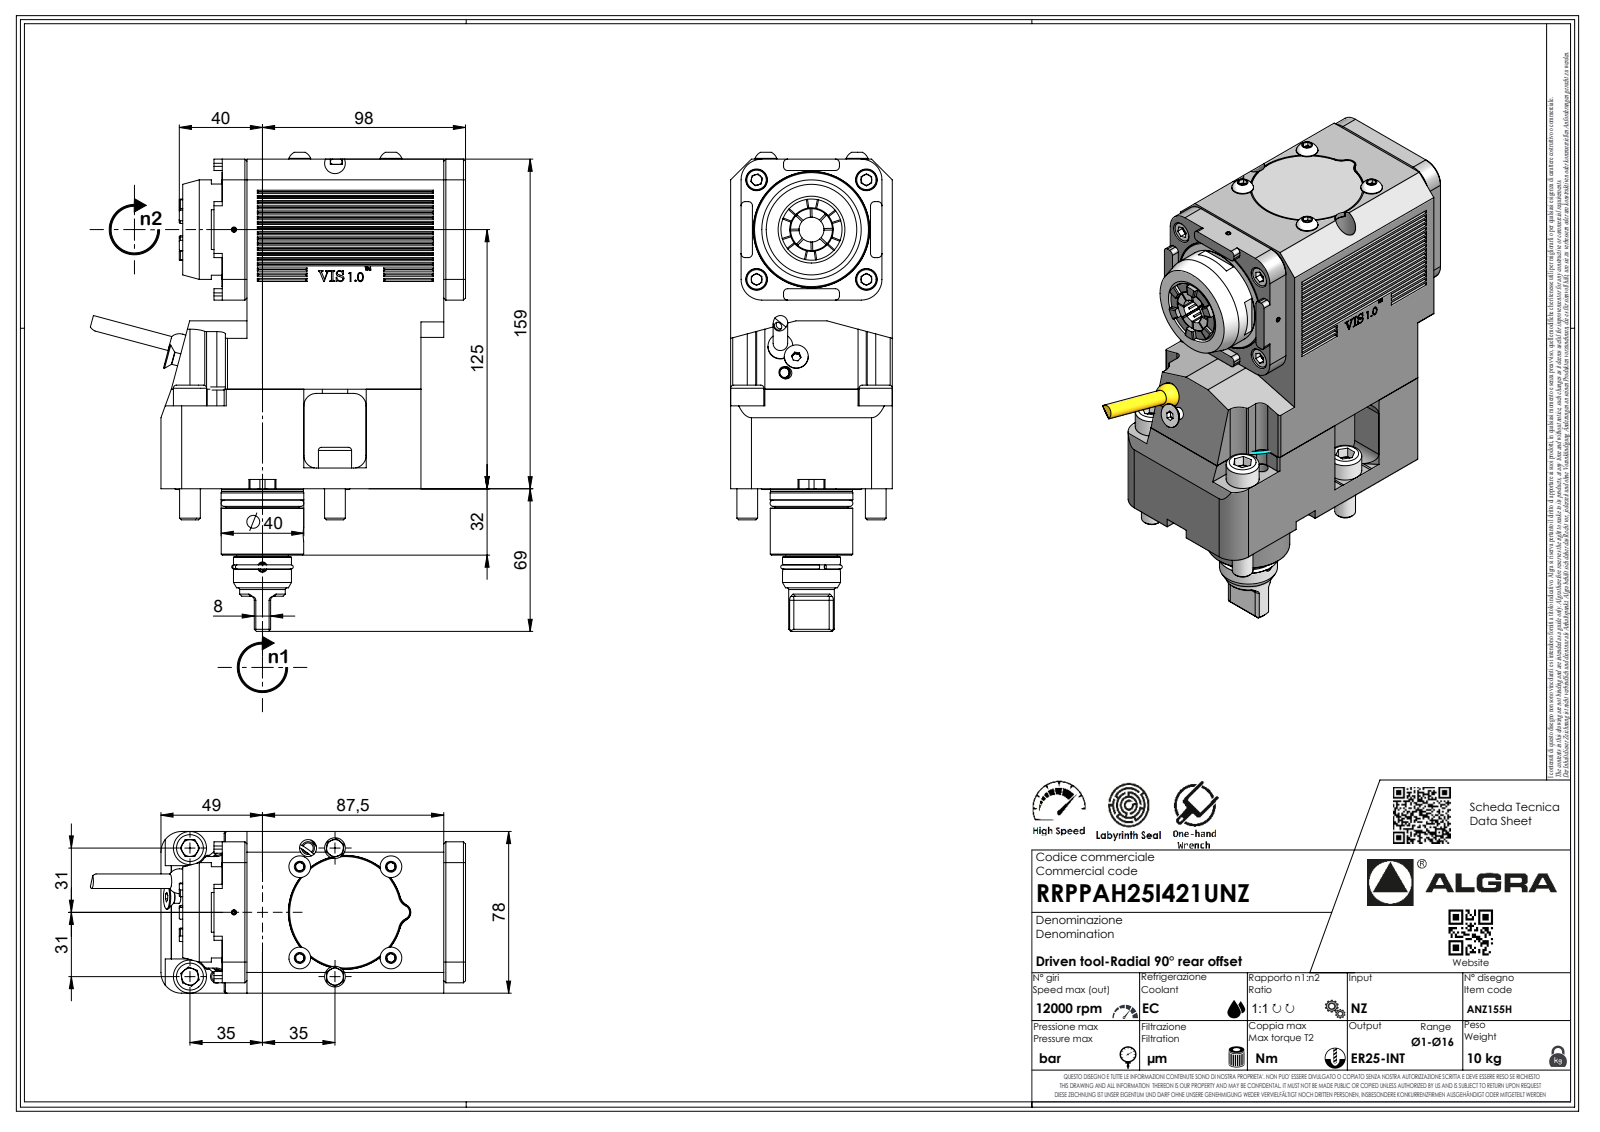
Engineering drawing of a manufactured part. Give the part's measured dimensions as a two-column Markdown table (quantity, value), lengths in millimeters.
| quantity | value |
| --- | --- |
| part name | RRPPAH25I421UNZ |
| STEP written by | SolidWorks 2023 (AUTOMOTIVE_DESIGN) |
| units | millimeters |
| bodies | 1 solid, 533 faces (344 planar, 92 cylindrical, 97 other) |
| overall size | 227.8 × 181.57 × 78 |
| volume | 1 510 000 mm³ |
| surface area | 98 575 mm² |
| round holes (diameter × count) | 2.1 × 1, 4 × 1 |
| round bosses / shafts (diameter × count) | 10 × 4, 16 × 2, 48 × 1, 39.9 × 1, 39.8 × 1, 39.5 × 1, 35.1 × 1, 28 × 1 |
| partial cylindrical surfaces (radius × count) | 2 × 23, 1 × 8, 0.33 × 7, 0.52 × 7, 3.7 × 7, 10 × 6, 3.5 × 2, 4.1 × 2 |
| main face-to-face distances | 78, 159, 22, 11, 73, 5, 68, 106, 125.5, 136.5 |
